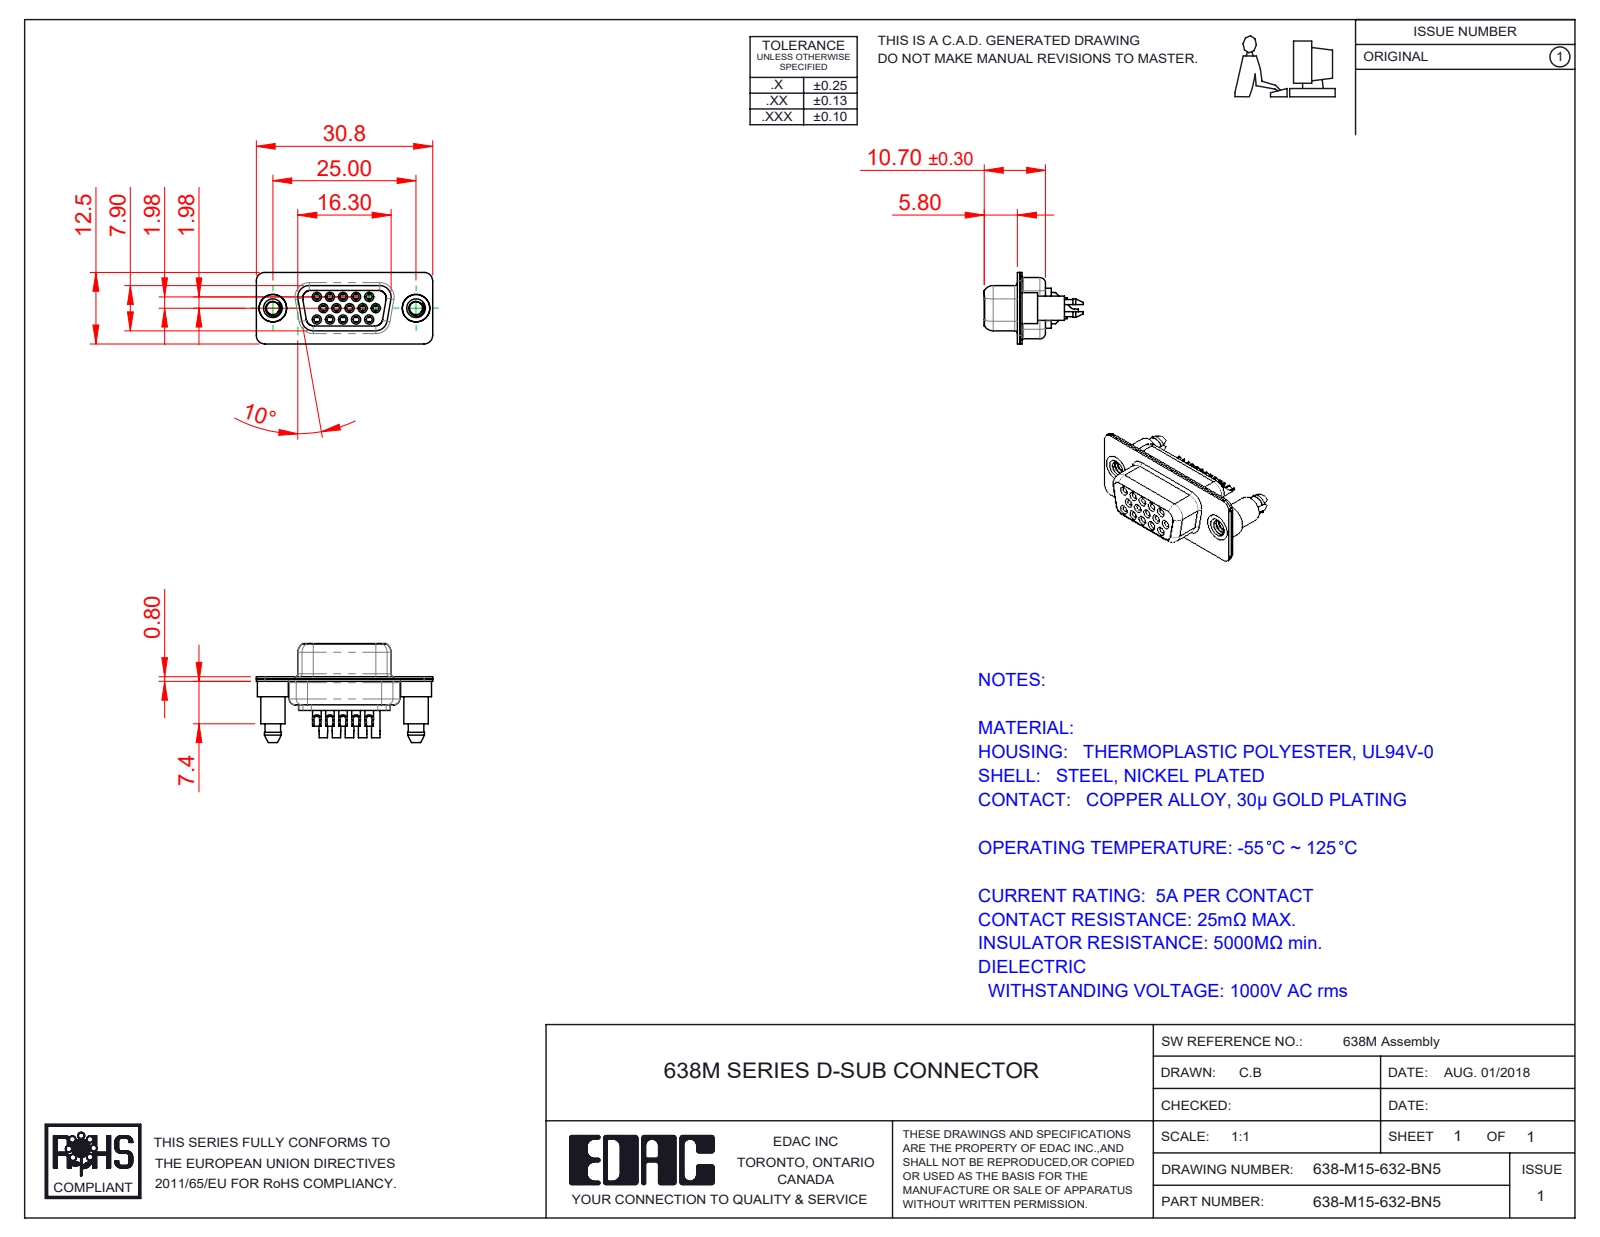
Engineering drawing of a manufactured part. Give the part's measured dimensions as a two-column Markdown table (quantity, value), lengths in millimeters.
| quantity | value |
| --- | --- |
| part name | 638M Shell Rear_15 Contacts; 638M Contact Row 2_32; 638M Contact Row 3_32; 638M Contact Row 1_32 (+4 more) |
| STEP written by | SolidWorks 2020 (CONFIG_CONTROL_DESIGN) |
| units | millimeters |
| bodies | 20 solids, 1154 faces (338 planar, 484 cylindrical, 332 other) |
| overall size | 30.8 × 17.3 × 12.5 |
| volume | 1 793 mm³ |
| surface area | 5 765 mm² |
| round holes (diameter × count) | 1 × 16, 1.1 × 15, 1.7 × 15, 1.8 × 15, 2 × 15, 2.26 × 2, 4 × 2, 4.8 × 2 |
| round bosses / shafts (diameter × count) | 2.2 × 15, 1.6 × 15, 1.5 × 15, 5.4 × 2, 4.9 × 2, 4.25 × 2 |
| partial cylindrical surfaces (radius × count) | 1.5 × 18, 2 × 12, 1.6 × 10, 1.35 × 8, 1 × 7, 0.25 × 4, 0.5 × 4, 0.6 × 4 |
| main face-to-face distances | 0.4, 1.4, 0.45, 8.45, 1, 0.8, 8.9, 1.8, 6.2, 7.05 |
| hole center spacings | 2.28, 3.96, 2.29, 4.57, 6.05, 6.04, 6.86, 7.92 |
